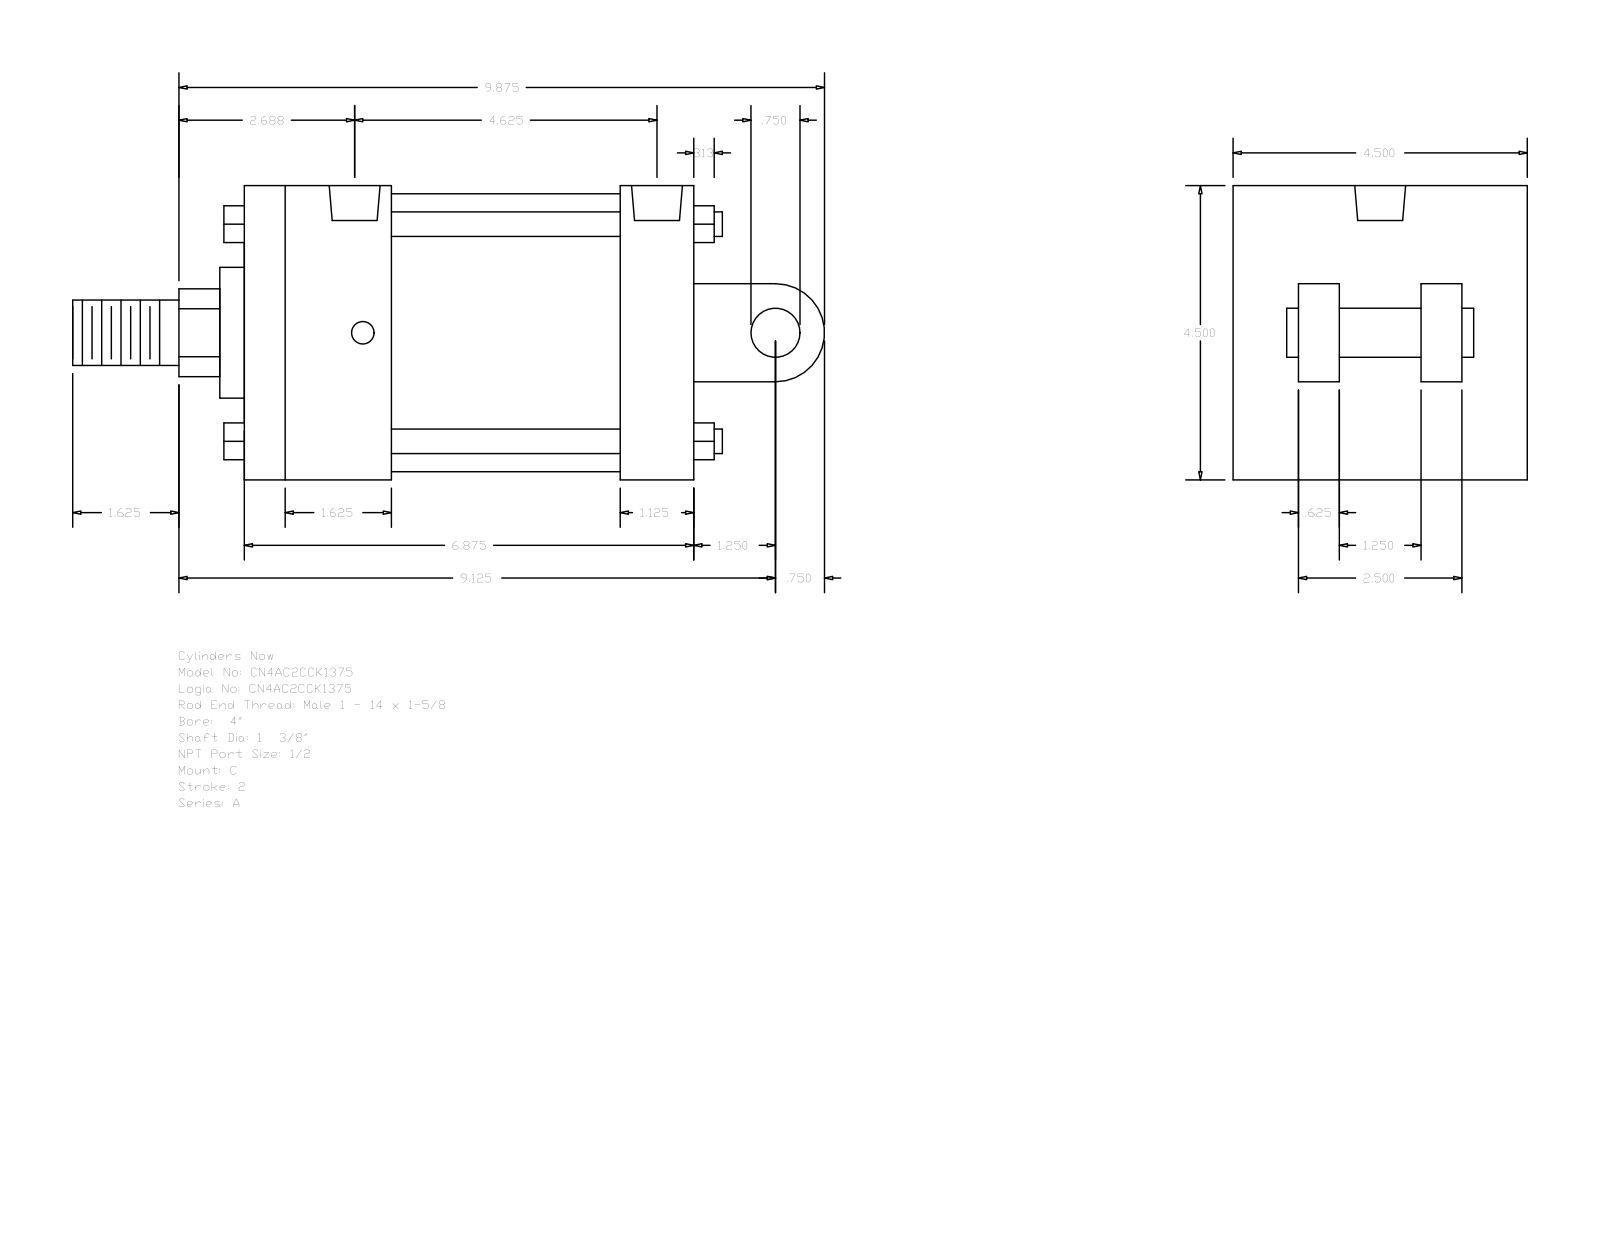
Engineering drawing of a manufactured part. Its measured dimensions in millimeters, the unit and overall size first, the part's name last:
Units: millimetres
Overall size (bounding box): 292.1 × 114.3 × 114.3
Round holes (diameter × count): ⌀8.73 ×4, ⌀19.77 ×2
Round bosses / shafts (diameter × count): ⌀9.53 ×4, ⌀107.95 ×1, ⌀50.8 ×1, ⌀34.92 ×1, ⌀25.4 ×1, ⌀19.05 ×1
Partial cylindrical surfaces — rounded edges, fillets, slot ends (radius × count): R17.06 ×1, R19.05 ×1
Main face-to-face distances: 114.3, 174.63, 88.9, 57.15, 28.58, 73.03, 146.05, 117.48, 41.27, 25.4
Hole centre spacings: 3.18, 111.12, 114.3, 117.48
Bodies: 0 solids, 135 faces (102 planar, 33 cylindrical, 0 other)
Part name (STEP PRODUCT): A_C__0400_1.375
STEP written by: GSSL Pune (CONFIG_CONTROL_DESIGN)
